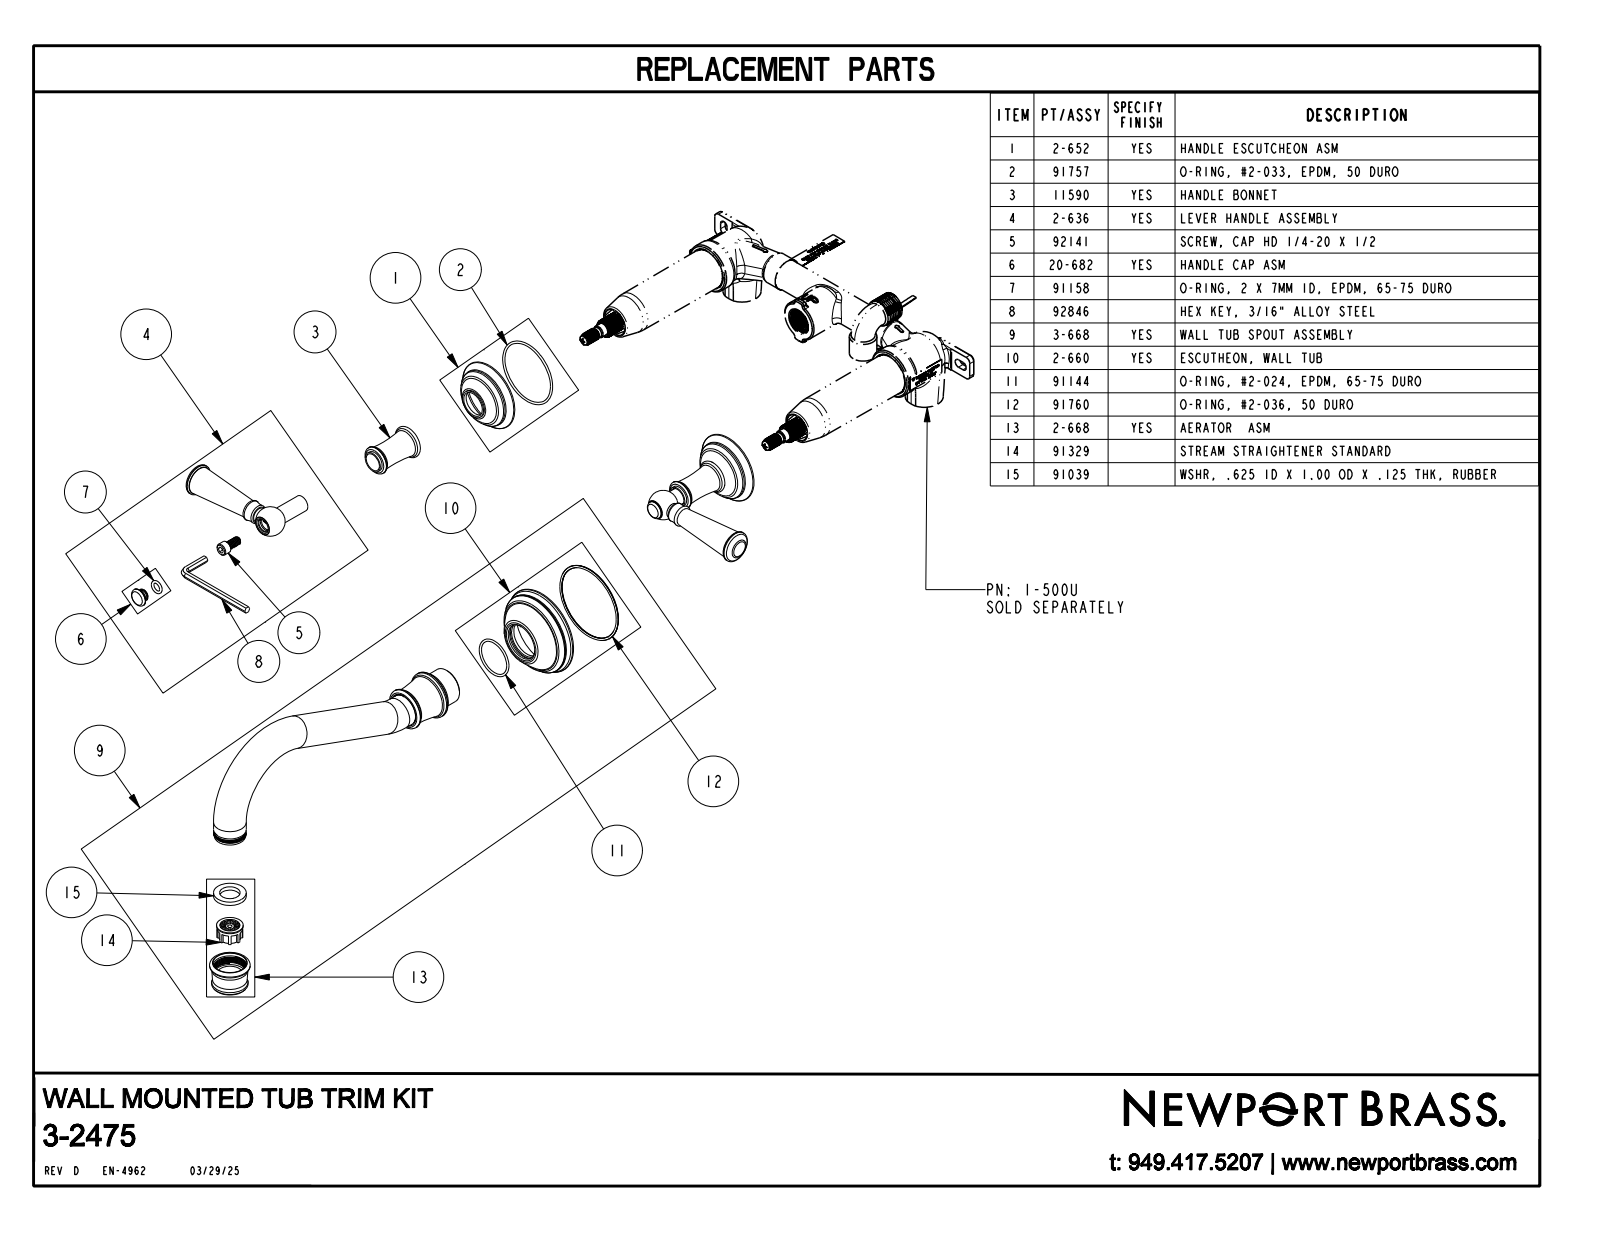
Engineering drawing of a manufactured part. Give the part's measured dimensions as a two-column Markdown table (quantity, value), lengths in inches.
| quantity | value |
| --- | --- |
| part name | 3-2475_SW0001 |
| STEP written by | CREO PARAMETRIC BY PTC INC, 2018400 (AUTOMOTIVE_DESIGN) |
| units | inches |
| bodies | 3 solids, 217 faces (25 planar, 36 cylindrical, 156 other) |
| overall size | 14.475 × 10.323 × 8.658 |
| volume | 21.46 in³ |
| surface area | 100.1 in² |
| round bosses / shafts (diameter × count) | 1 × 3, 0.9 × 2, 0.649 × 2, 0.56 × 2, 0.517 × 2, 1.5 × 1, 1.32 × 1, 1.3 × 1 |
| main face-to-face distances | 2.14, 2.2, 0.06, 2.22, 0.08, 0.02, 1.004, 1.136, 1.196, 1.216 |
